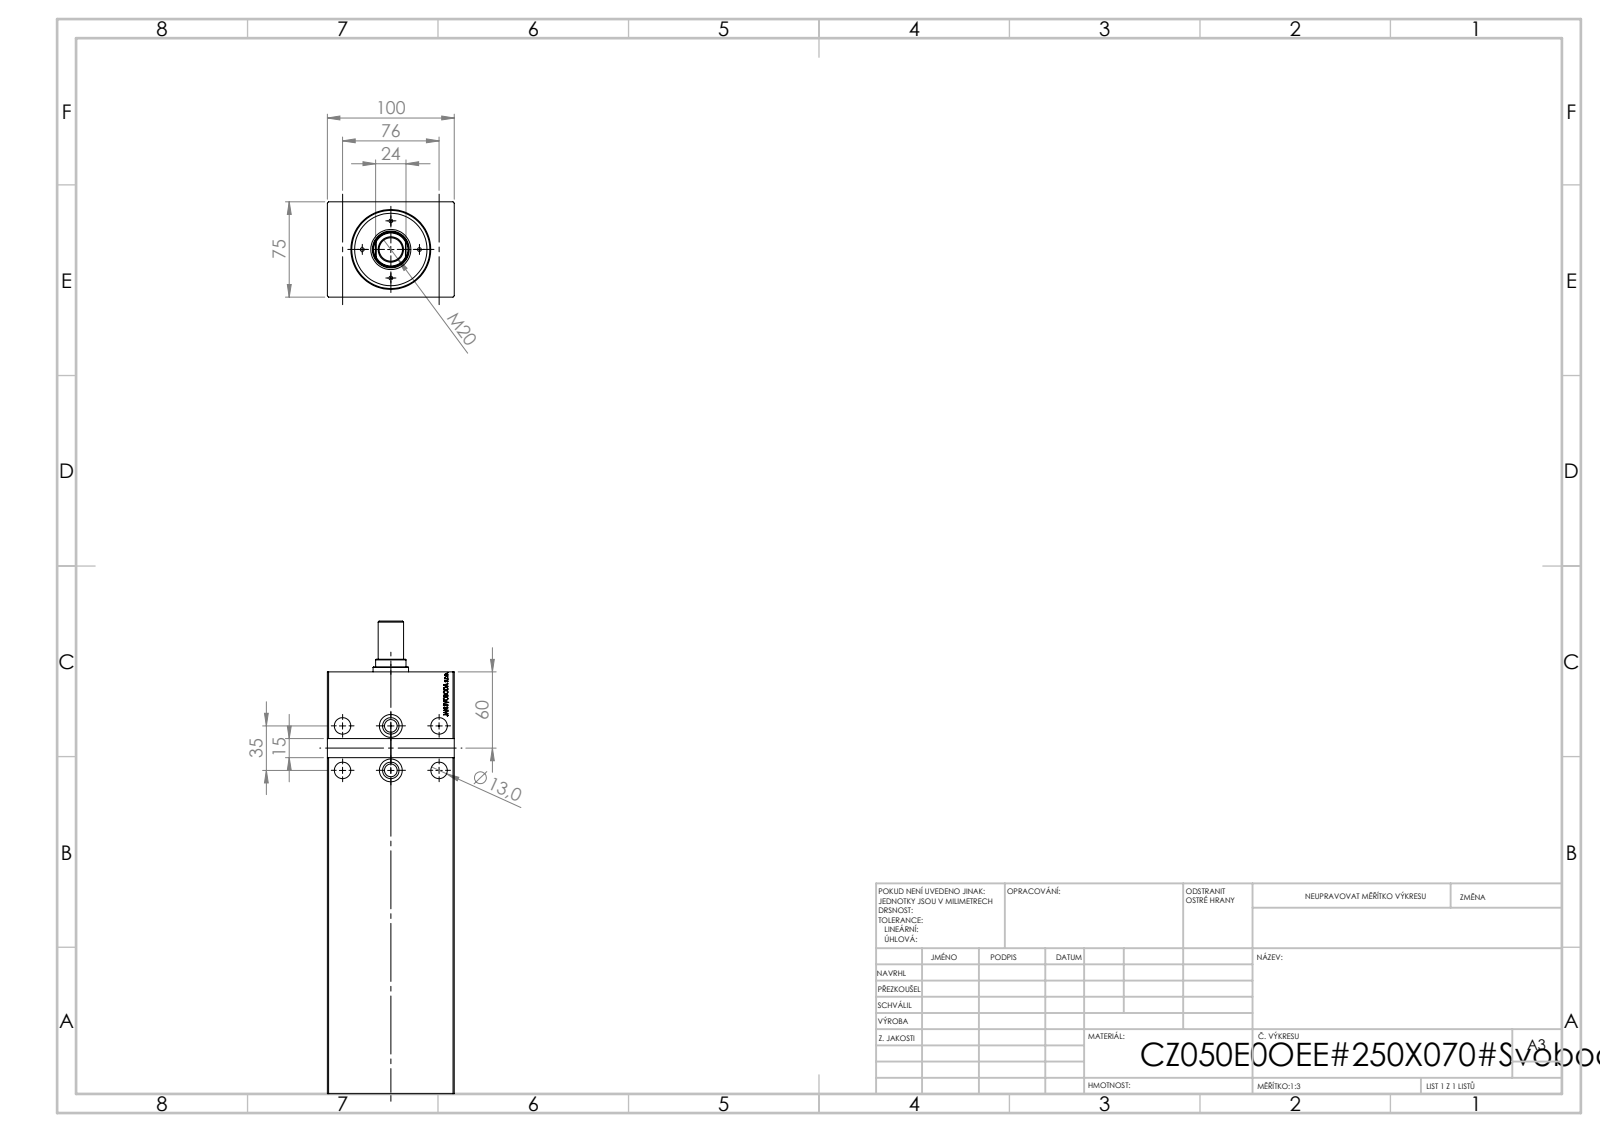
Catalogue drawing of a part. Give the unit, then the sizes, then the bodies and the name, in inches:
Units: inches
Overall size (bounding box): 13.071 × 3.937 × 2.953
Round holes (diameter × count): ⌀0.512 ×4, ⌀0.315 ×2, ⌀0.394 ×2, ⌀0.709 ×2, ⌀1.417 ×1, ⌀1.969 ×1, ⌀2.421 ×1
Round bosses / shafts (diameter × count): ⌀0.512 ×2
Main face-to-face distances: 2.953, 3.937, 13.071, 12.37, 0.701, 0.079, 2.874, 13.063, 0.693, 0.394
Hole centre spacings: 1.496, 2.034, 1.378, 2.992, 3.294, 0.741, 0.817, 1.745
Volume: 110.9 in³ · Surface area: 298.2 in²
Bodies: 1 solid, 807 faces (395 planar, 30 cylindrical, 382 other)
STEP written by: SolidWorks 2019 (CONFIG_CONTROL_DESIGN)
